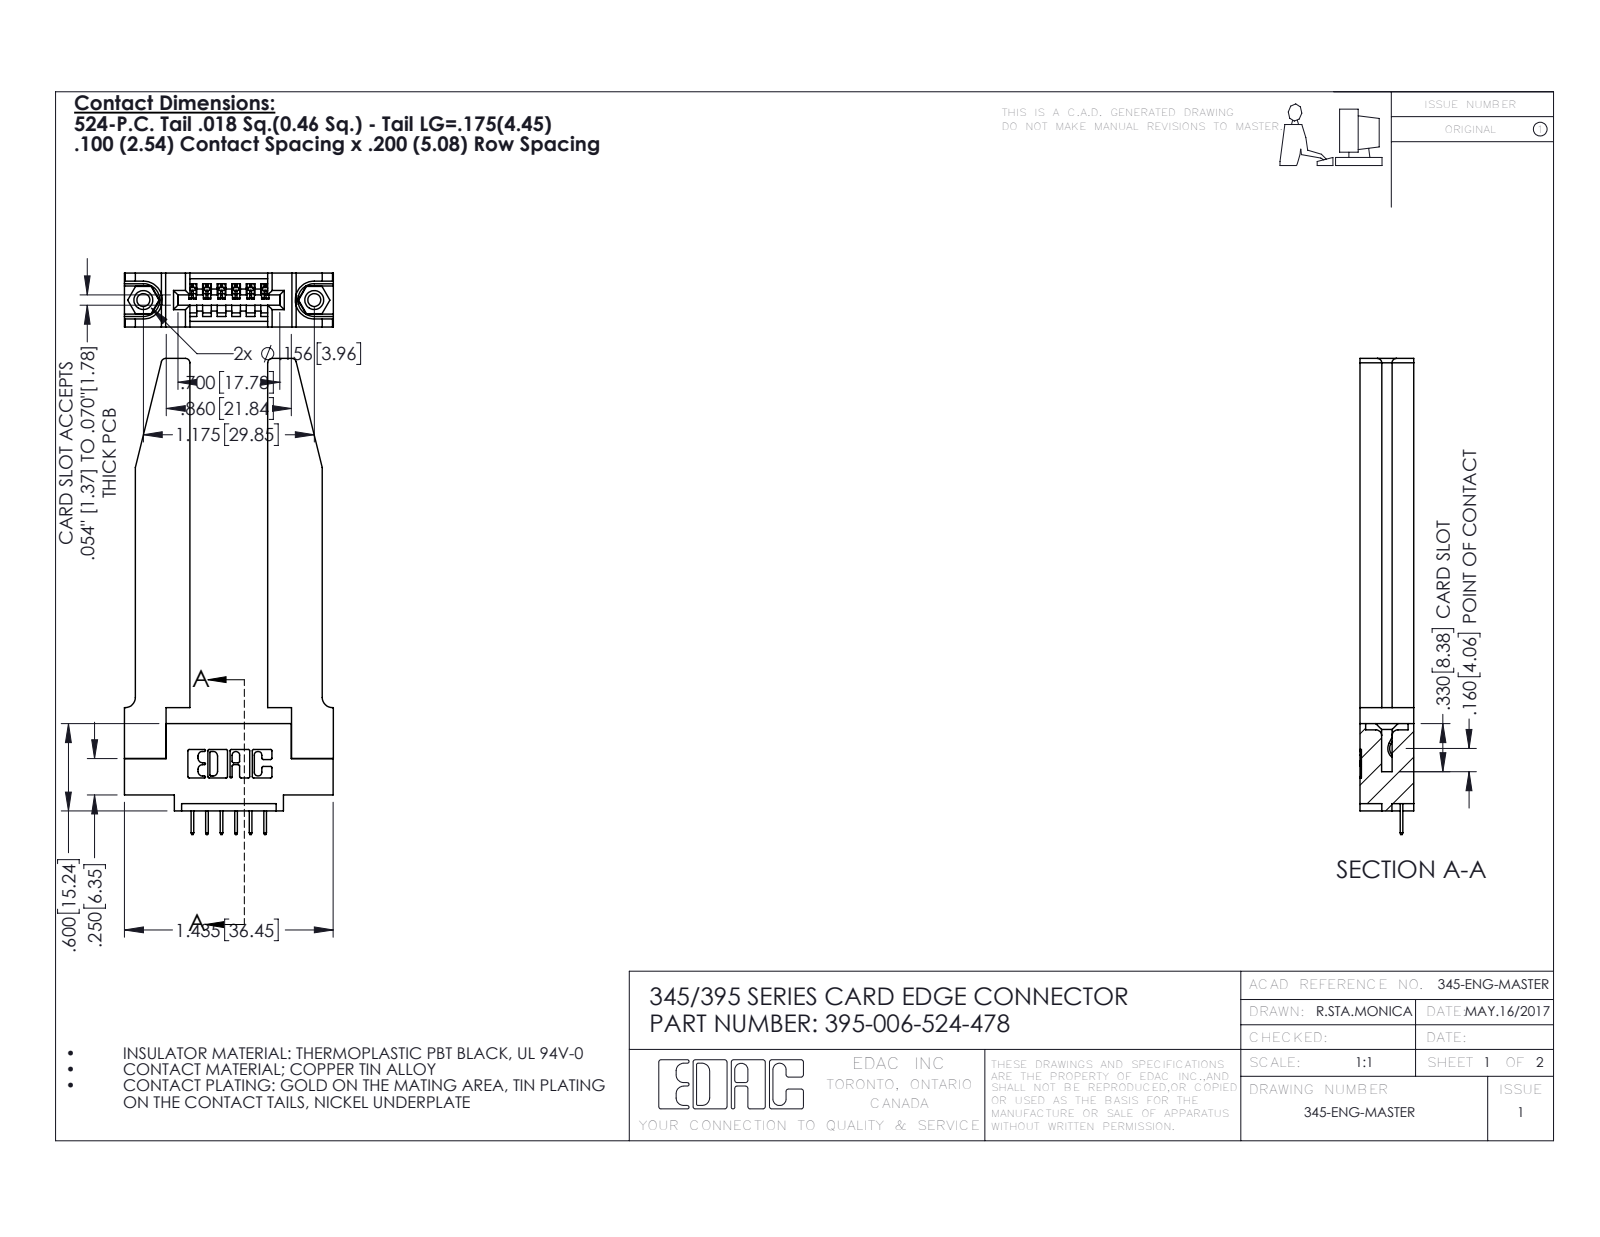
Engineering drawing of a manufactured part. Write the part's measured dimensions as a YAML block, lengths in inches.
part_name: "345 Part_0.110 Offset - 0.156 Dia-TH; 395-006-524-478; 345-292-001_345-293-124; 345-220-078_345-220-078 (+1 more)"
step_written_by: "SolidWorks 2016 (CONFIG_CONTROL_DESIGN)"
units: inches
bodies: {solids: 11, faces: 736, planar: 502, cylindrical: 182, other: 52}
overall_size: [3.272, 1.436, 0.37]
volume: 0.662
surface_area: 16.19
round_holes:
  - {diameter: 0.089, count: 2}
  - {diameter: 0.125, count: 2}
  - {diameter: 0.156, count: 2}
  - {diameter: 0.064, count: 1}
round_bosses_or_shafts:
  - {diameter: 0.155, count: 2}
partial_cylinders:
  - {radius: 0.01, count: 22}
  - {radius: 0.006, count: 12}
  - {radius: 0.03, count: 8}
  - {radius: 0.007, count: 6}
  - {radius: 0.031, count: 6}
  - {radius: 0.026, count: 3}
  - {radius: 0.031, count: 2}
  - {radius: 0.04, count: 2}
face_to_face_distances: [0.37, 0.15, 0.22, 0.535, 0.072, 0.148, 0.298, 0.077, 0.071, 0.055]
hole_center_spacings: [0.27, 0.946, 1.175]
